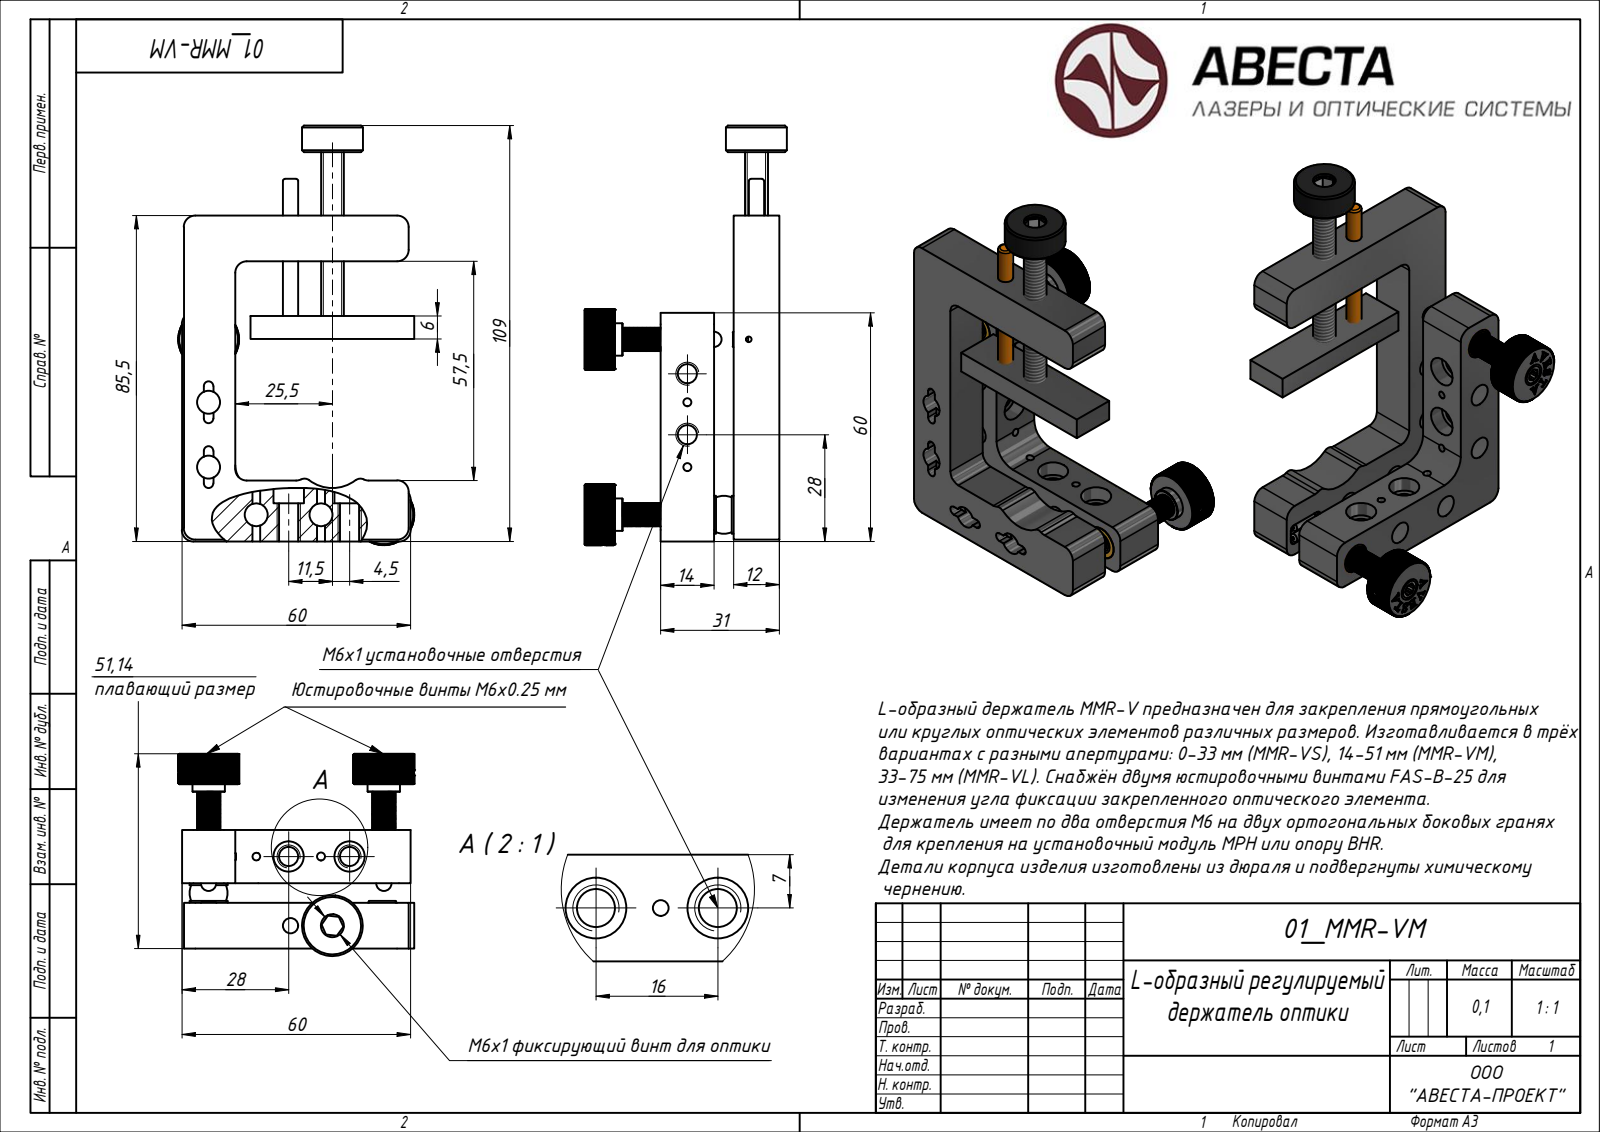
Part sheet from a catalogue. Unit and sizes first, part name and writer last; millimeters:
Units: millimetres
Overall size (bounding box): 110.14 × 62 × 48.2
Main face-to-face distances: 12, 14, 13.5, 0.5, 19.14, 31.14, 17.14, 5.14, 59.5, 6
Volume: 54 267 mm³ · Surface area: 29 882 mm²
Bodies: 18 solids, 723 faces (323 planar, 0 cylindrical, 400 other)
STEP written by: ST-DEVELOPER v15 (AUTOMOTIVE_DESIGN)
